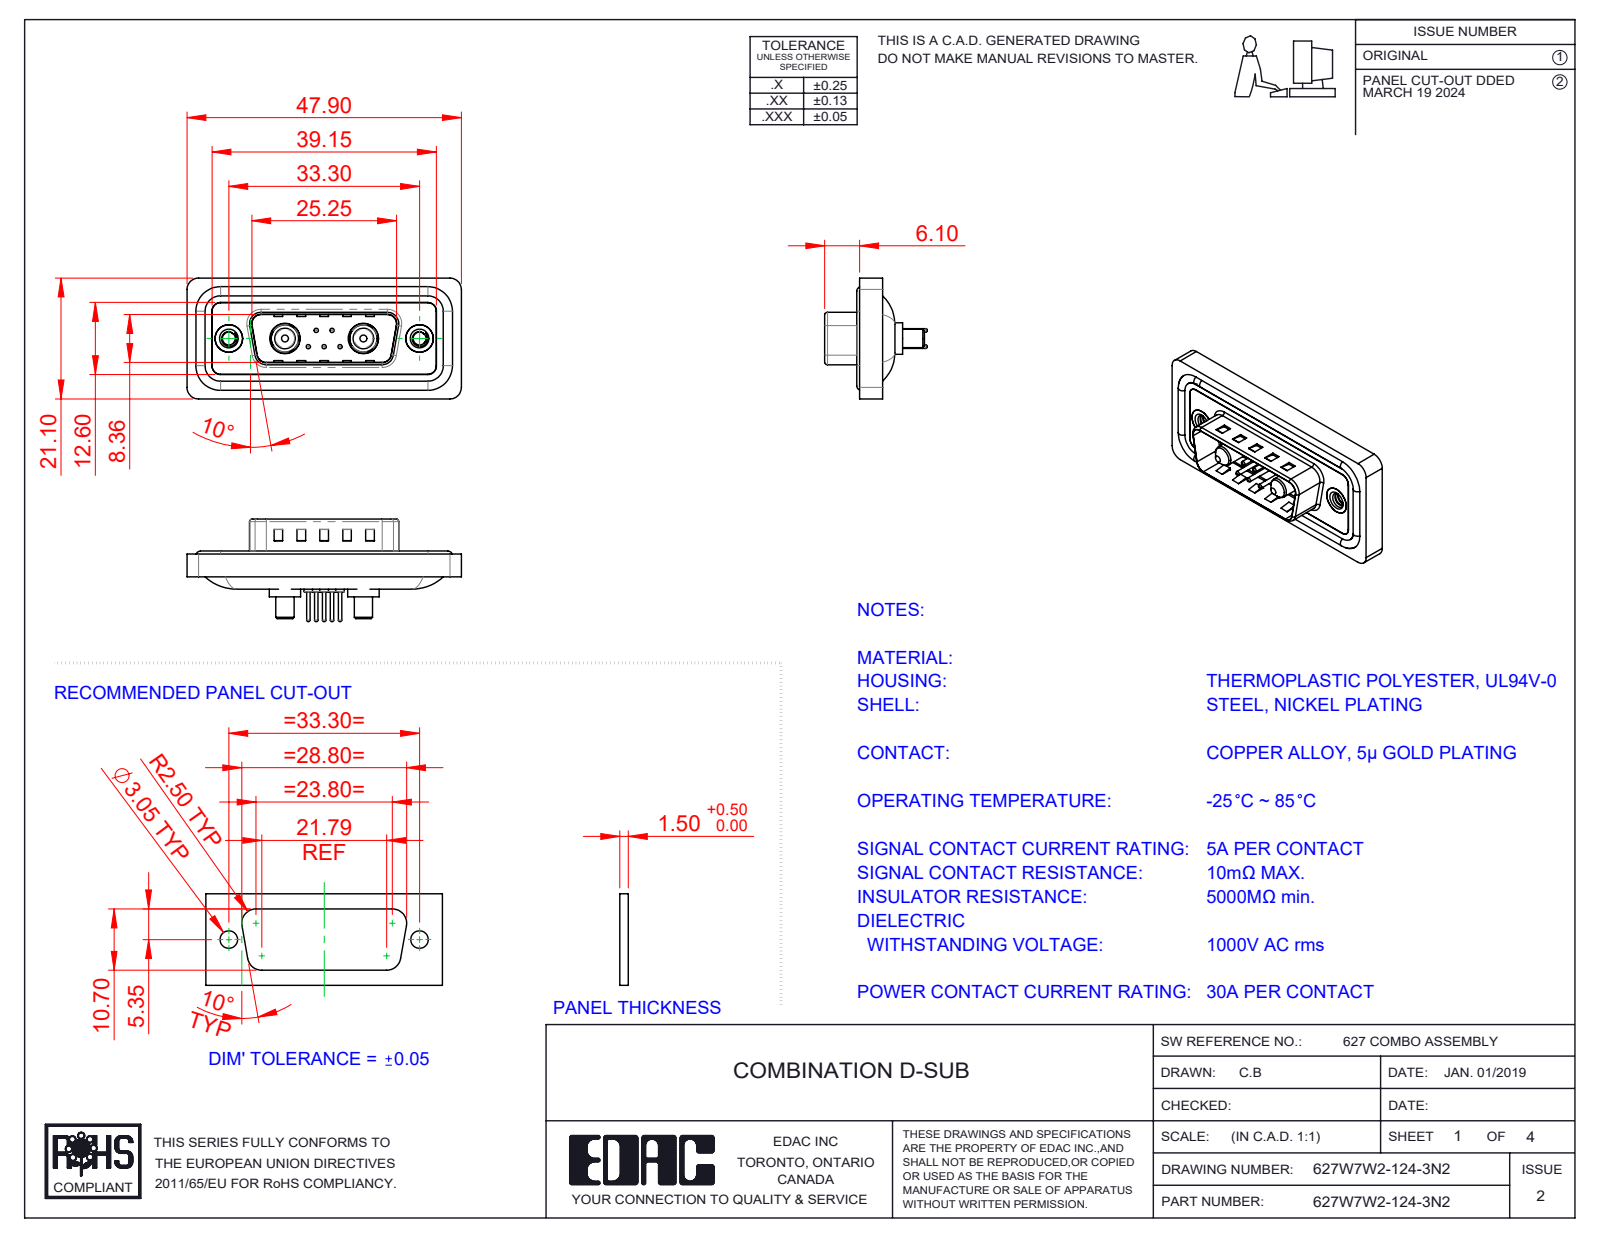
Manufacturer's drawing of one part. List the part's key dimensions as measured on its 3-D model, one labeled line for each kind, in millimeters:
Part name (STEP PRODUCT): 627Combo Threaded Rivet_2; 627Combo Housing_7W2; 627Combo Waterproof Housing_15 Contacts; 627Combo Contact Row 1_24 (+5 more)
STEP written by: SolidWorks 2023 (CONFIG_CONTROL_DESIGN)
Units: millimetres
Bodies: 16 solids, 710 faces (232 planar, 292 cylindrical, 186 other)
Overall size (bounding box): 47.9 × 21.1 × 17.9
Volume: 5 531 mm³ · Surface area: 8 802 mm²
Round holes (diameter × count): ⌀0.75 ×5, ⌀1.6 ×5, ⌀2 ×5, ⌀2.26 ×2, ⌀4 ×2, ⌀4.8 ×2, ⌀4.85 ×2, ⌀5 ×2, ⌀5.3 ×2
Round bosses / shafts (diameter × count): ⌀1.5 ×5, ⌀0.6 ×5, ⌀1.6 ×4, ⌀5.5 ×2, ⌀5.2 ×2, ⌀4.9 ×2, ⌀4.75 ×2, ⌀3.75 ×2
Partial cylindrical surfaces — rounded edges, fillets, slot ends (radius × count): R1.5 ×26, R2 ×20, R0.5 ×8, R1.6 ×8, R0.25 ×4, R0.6 ×4, R0.65 ×4, R0.9 ×4
Main face-to-face distances: 0.4, 1.1, 1.5, 1.6, 0.5, 3.1, 2.9, 0.82, 9.58, 2.5
Hole centre spacings: 3.16, 2.77, 9.8, 23.5, 4.31, 4.33, 5.03, 5.04
